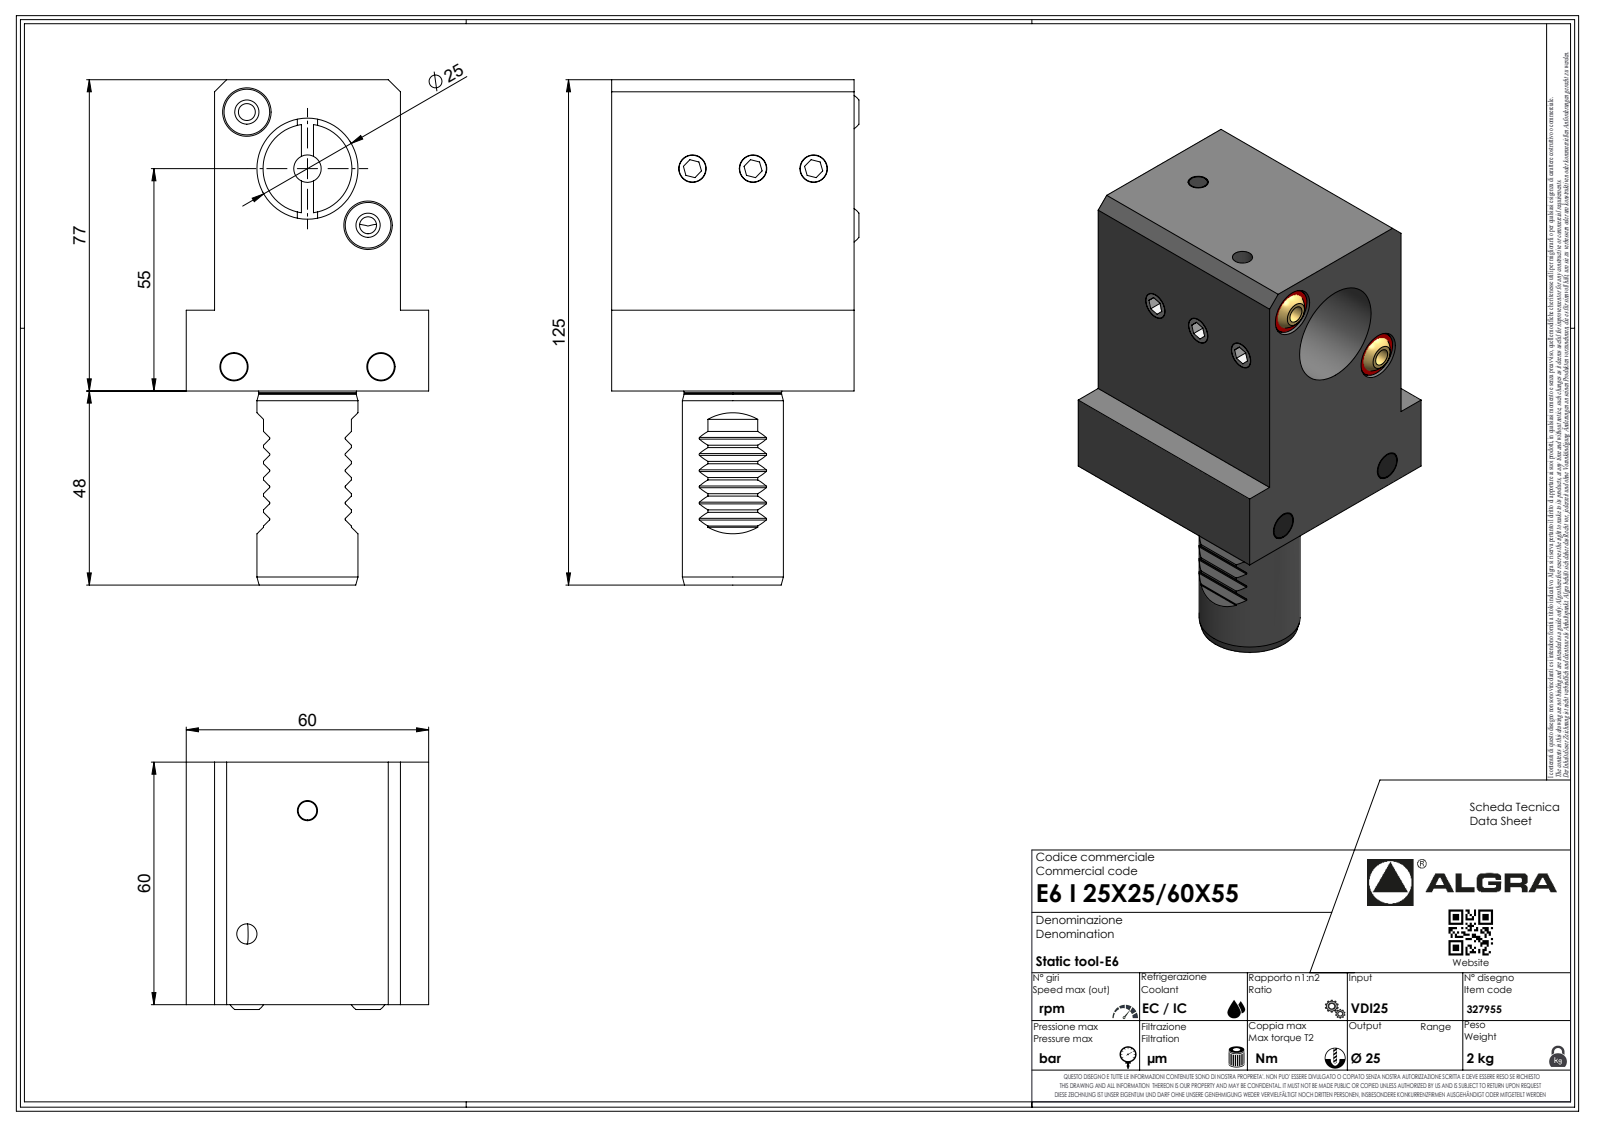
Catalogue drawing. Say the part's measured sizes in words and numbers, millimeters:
The part is named "327955". Its 3-D file was written by "SolidWorks 2023 (AUTOMOTIVE_DESIGN)". It is 1 solid with 254 faces: 162 planar, 35 cylindrical and 57 other. Overall it measures 125 by 61.2 by 60 millimeters. Its volume is 227 112 cubic millimeters and its surface area 31 780 square millimeters. Round holes: 1 of diameter 2.1, 1 of diameter 25. Round bosses or shafts: 1 of diameter 25, 1 of diameter 24.1, 1 of diameter 6.37, 1 of diameter 1.7. Partial cylindrical surfaces (rounded edges, fillets, slot ends): 7 of radius 0.33, 7 of radius 0.52, 7 of radius 3.7, 6 of radius 0.3, 1 of radius 0.21. The main face-to-face distances are 60, 46, 7, 53, 77, 20, 57, 10, 50, 48.
